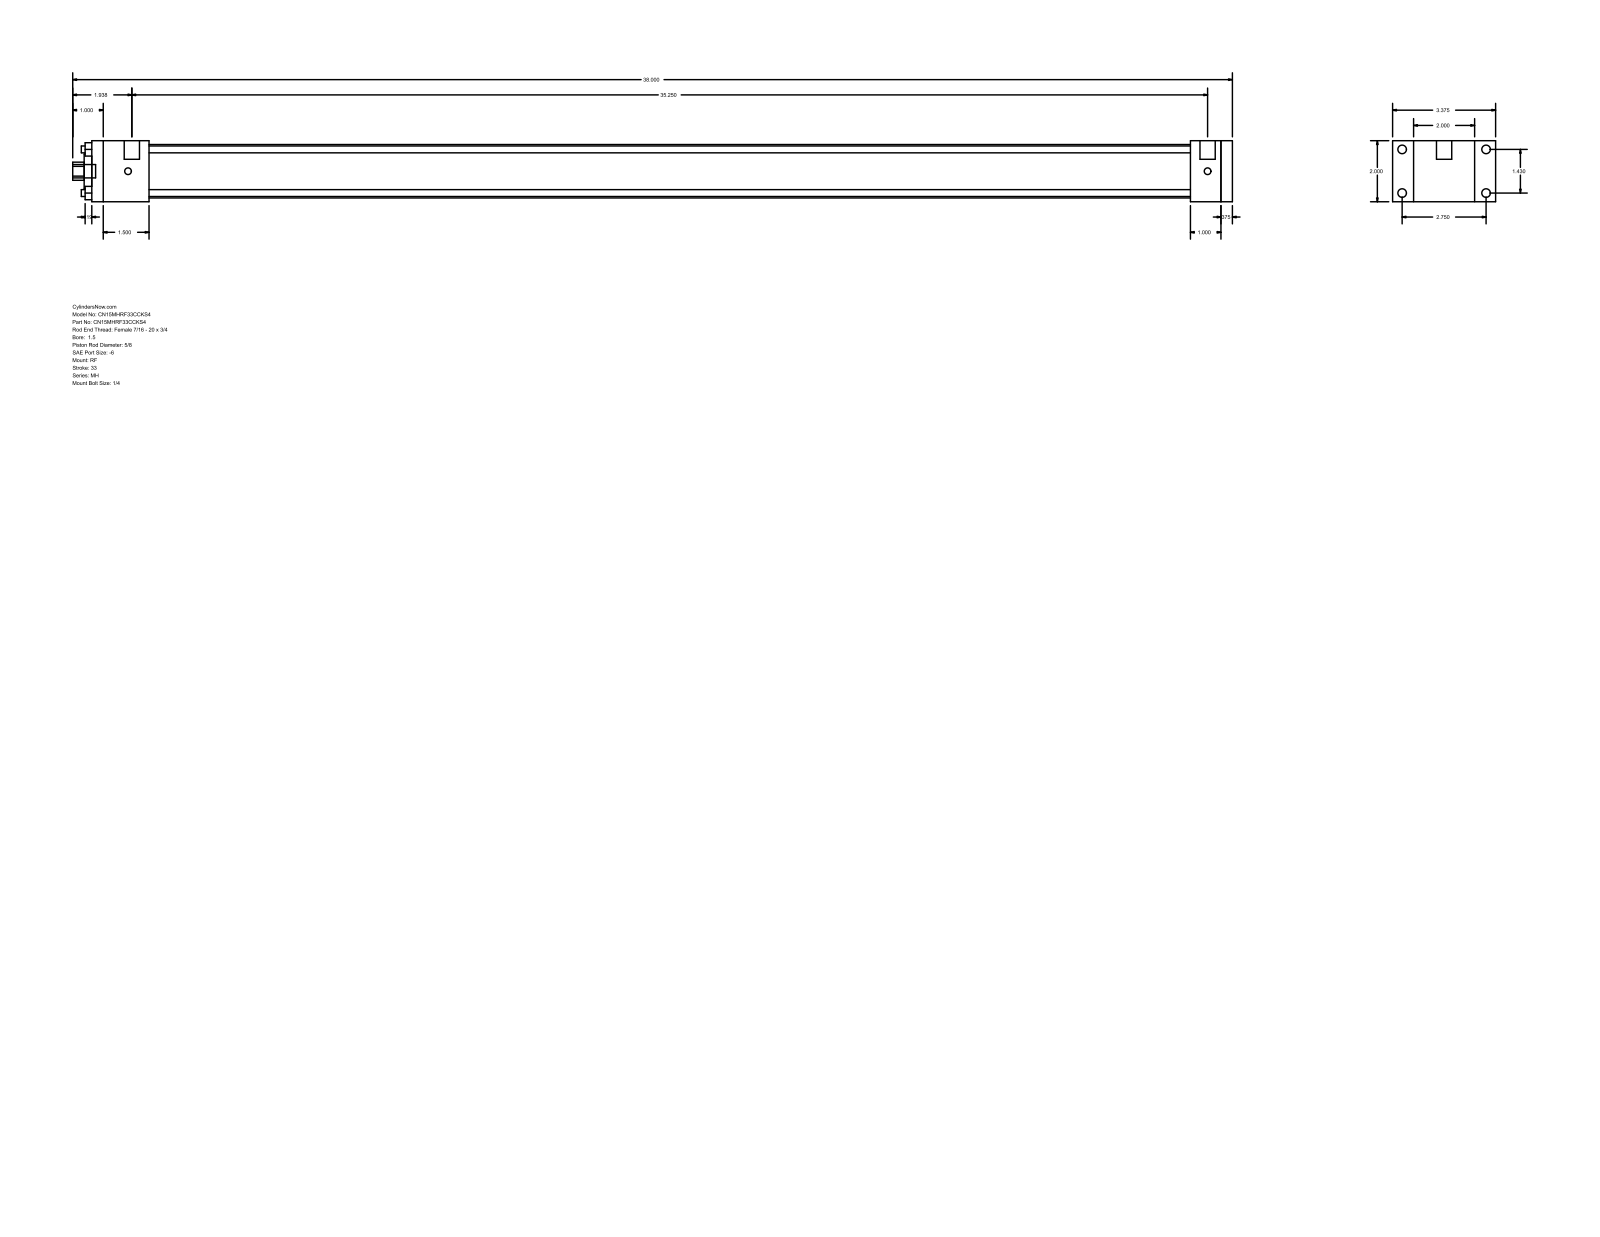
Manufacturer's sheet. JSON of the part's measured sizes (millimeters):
{"part_name": "MH_RF__0150_0.625", "step_written_by": "GSSL Pune (CONFIG_CONTROL_DESIGN)", "units": "millimeters", "bodies": {"solids": 0, "faces": 92, "planar": 64, "cylindrical": 28, "other": 0}, "overall_size": [965.2, 85.72, 50.8], "round_holes": [[5.71, 4], [15.88, 1], [28.57, 1], [44.45, 1]], "round_bosses_or_shafts": [[7.14, 4], [5.56, 4], [12.7, 2], [11.11, 1]], "partial_cylinders_radius": [[7.54, 1]], "face_to_face_distances": [50.8, 9.53, 949.32, 939.79, 17.46, 68.26, 914.39, 25.4, 34.93, 47.62], "hole_center_spacings": [25.68, 36.32, 51.36]}
